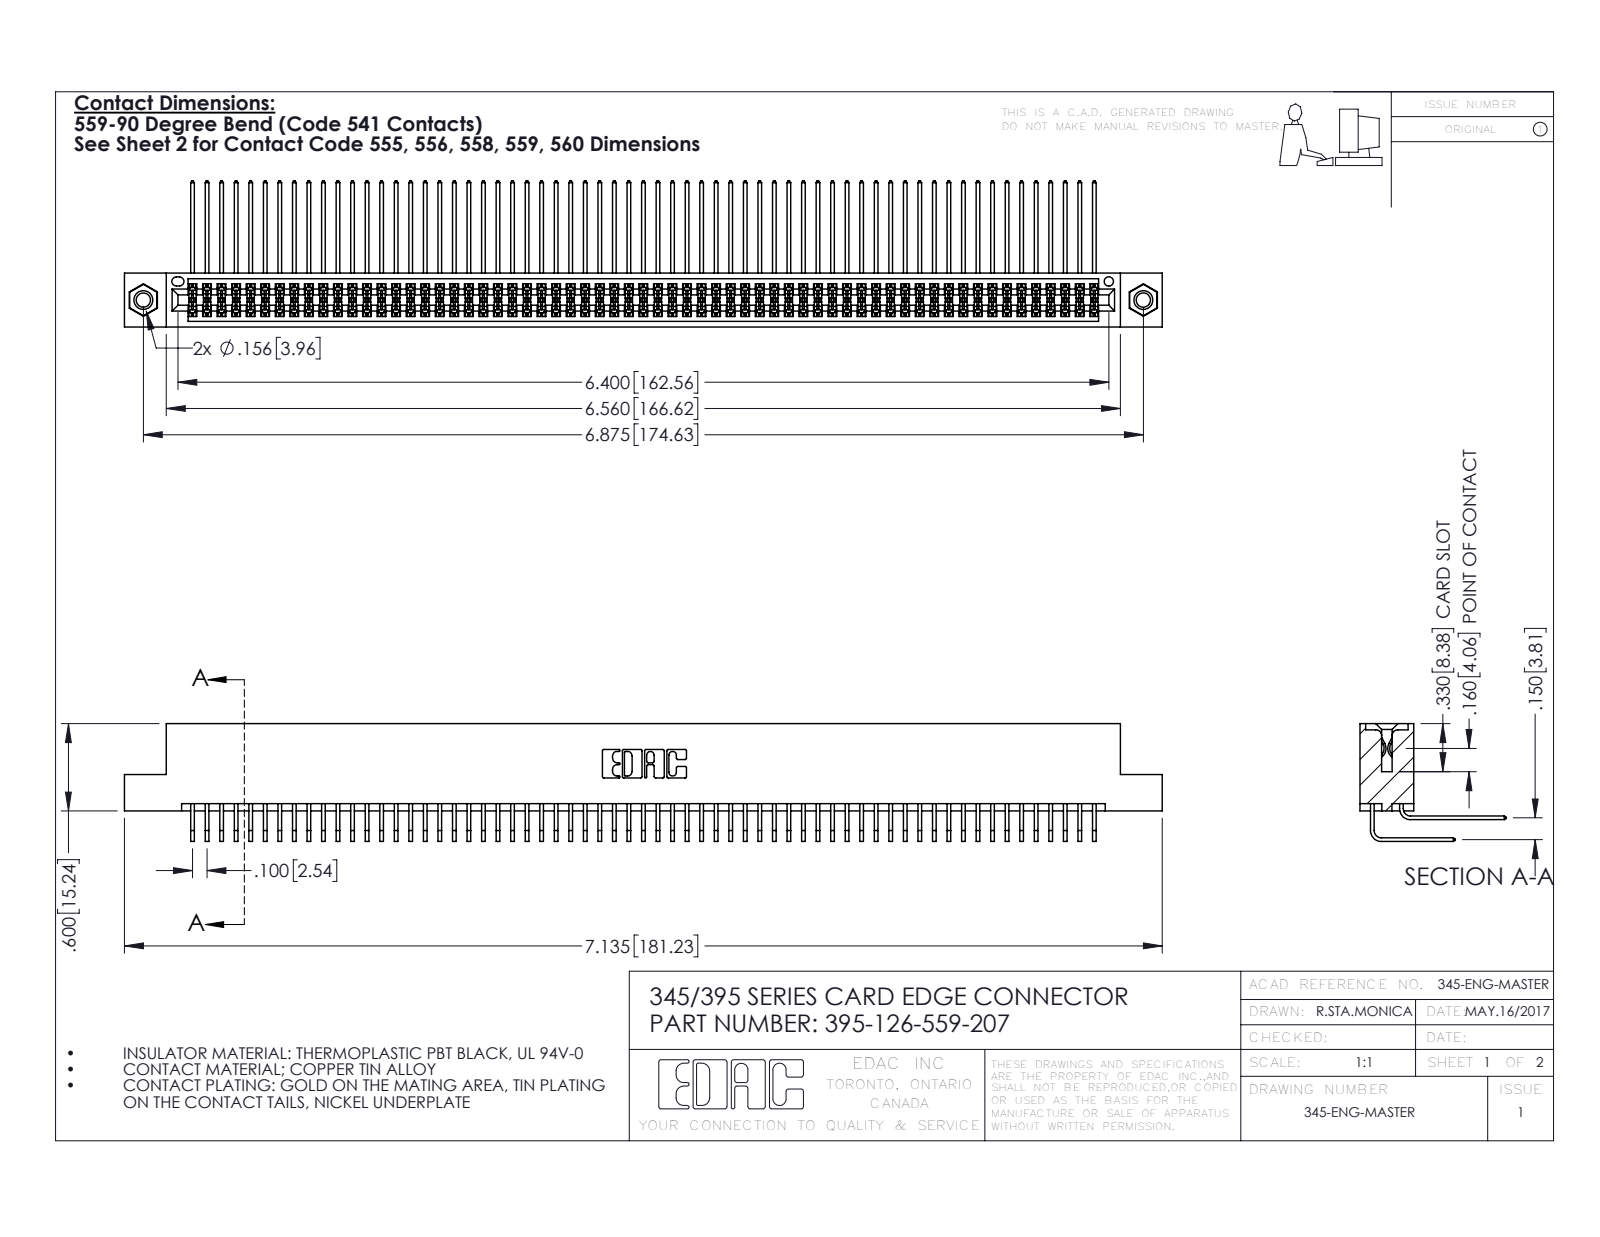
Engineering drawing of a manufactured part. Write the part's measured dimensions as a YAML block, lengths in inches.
part_name: "345-292-001_559 Tail - 2; 345-250-001_345-250-005-103; 345-292-001_558 559 Tail - 1; 345 Part_Flush Mounting Lugs - 0.156 Dia-TI (+1 more)"
step_written_by: "SolidWorks 2016 (CONFIG_CONTROL_DESIGN)"
units: inches
bodies: {solids: 129, faces: 6738, planar: 4522, cylindrical: 2200, other: 16}
overall_size: [7.135, 1.005, 0.809]
volume: 1.13
surface_area: 48.39
round_holes:
  - {diameter: 0.098, count: 2}
  - {diameter: 0.125, count: 2}
  - {diameter: 0.156, count: 2}
  - {diameter: 0.064, count: 1}
round_bosses_or_shafts:
  - {diameter: 0.155, count: 2}
partial_cylinders:
  - {radius: 0.006, count: 190}
  - {radius: 0.01, count: 22}
  - {radius: 0.007, count: 6}
  - {radius: 0.031, count: 6}
  - {radius: 0.026, count: 3}
  - {radius: 0.014, count: 2}
  - {radius: 0.019, count: 2}
  - {radius: 0.022, count: 2}
face_to_face_distances: [0.072, 0.298, 0.2, 0.37, 0.098, 0.272, 0.025, 0.225, 0.175, 0.15]
hole_center_spacings: [0.27, 6.639, 6.875]
